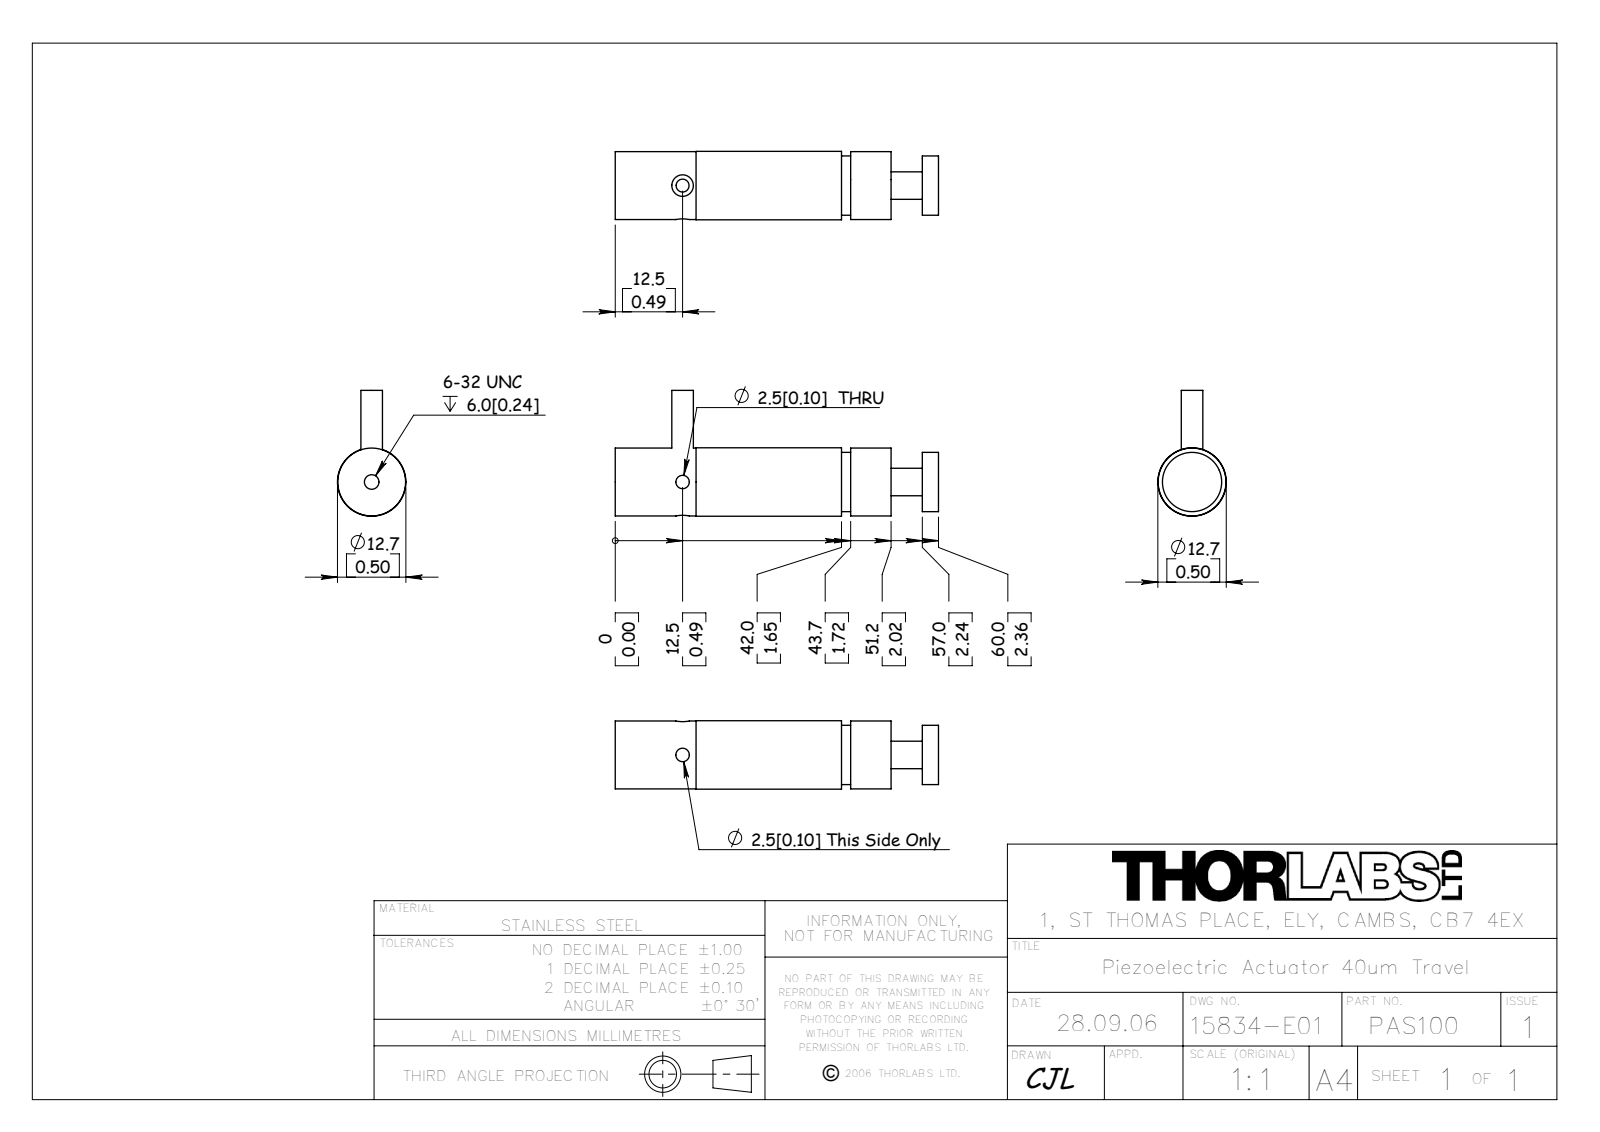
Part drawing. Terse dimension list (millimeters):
name: 15834-E0W
written by: SolidWorks 2007 (AUTOMOTIVE_DESIGN)
unit: mm
bodies: 0 solids, 37 faces (11 planar, 26 cylindrical, 0 other)
size: 60 × 23.35 × 12.7
holes: 2× ⌀2.5, 1× ⌀2.4, 1× ⌀2.71, 1× ⌀5.3, 1× ⌀9.55
bosses: 1× ⌀12.7, 1× ⌀12.6, 1× ⌀11, 1× ⌀5.1, 1× ⌀4
face distances: 51.2, 8.8, 60, 3, 5.8, 57, 15, 42, 50, 47
